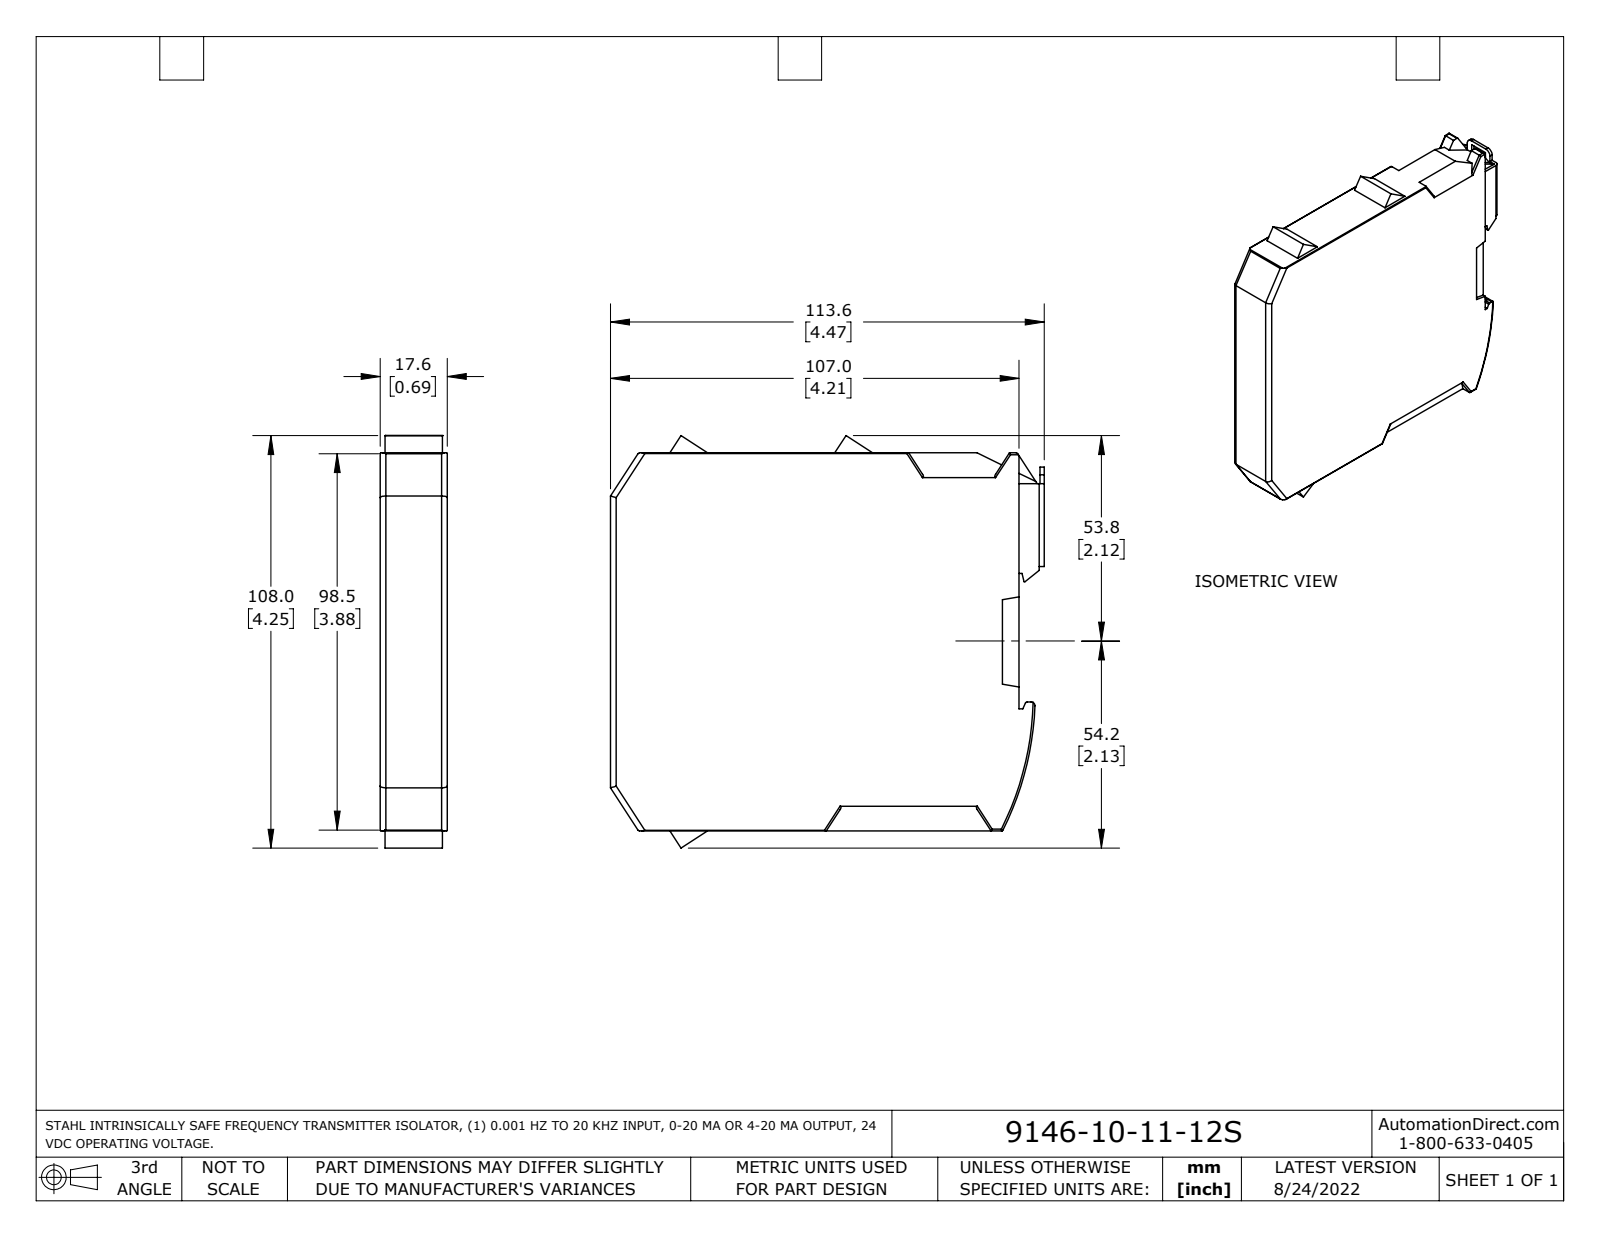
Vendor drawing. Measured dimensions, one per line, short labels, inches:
name: 9146-10-11-12S
written by: SolidWorks 2021 (AUTOMOTIVE_DESIGN)
unit: in
bodies: 2 solids, 173 faces (119 planar, 52 cylindrical, 2 other)
size: 4.472 × 4.252 × 0.693
volume: 11.4 in³; area: 46.44 in²
rounds: 17× R0.02, 6× R0.059, 4× R0.008, 4× R0.028, 2× R0.051, 2× R0.079, 1× R0.039, 1× R3.15
face distances: 0.693, 3.898, 4.213, 0.041, 0.652, 0.217, 4.429, 0.043, 0.26, 4.472
